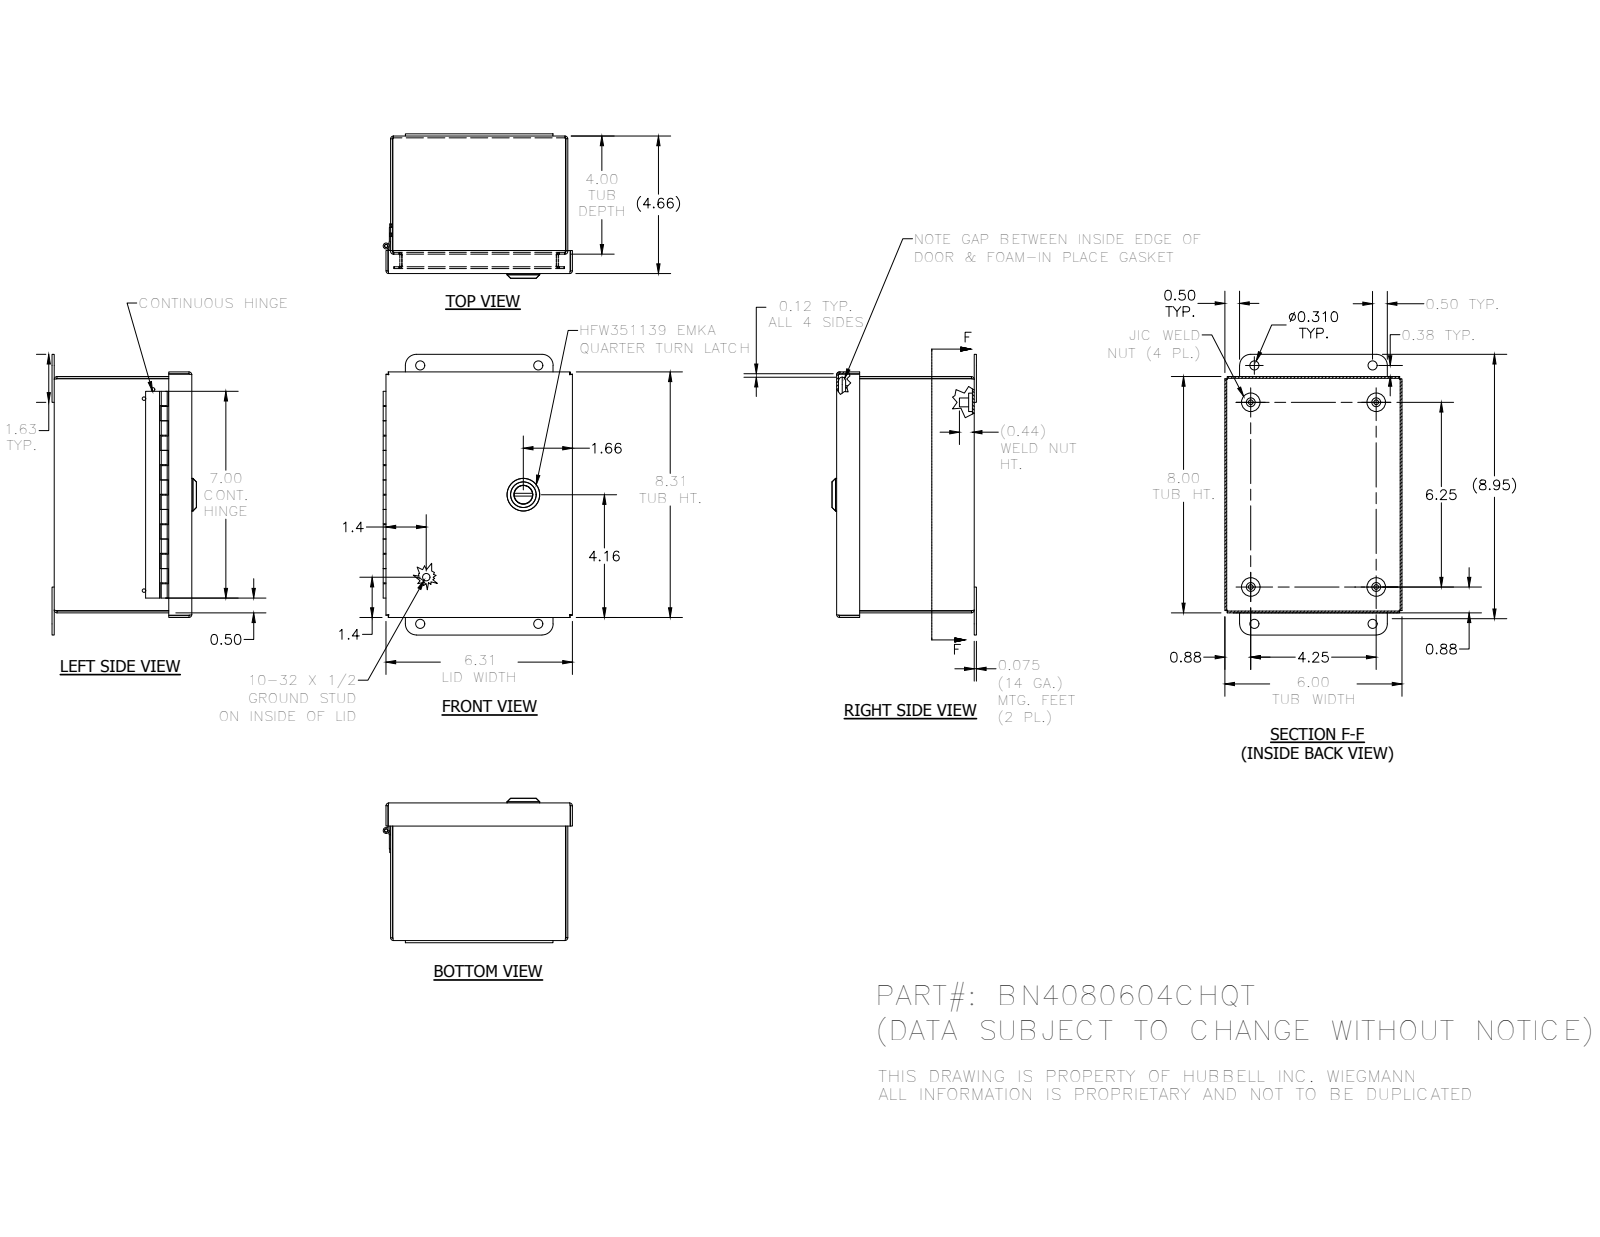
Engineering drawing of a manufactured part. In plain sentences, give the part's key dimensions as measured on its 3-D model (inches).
The part is named "BN4080604CHQT_a". Its 3-D file was written by "SolidWorks 2018 (AUTOMOTIVE_DESIGN)". It is 21 solids with 745 faces: 372 planar, 245 cylindrical and 128 other. Overall it measures 9.5 by 6.406 by 4.888 inches. Its volume is 20.9 cubic inches and its surface area 625 square inches. Round holes: 4 of diameter 0.156, 4 of diameter 0.31, 3 of diameter 0.12, 1 of diameter 0.116, 1 of diameter 0.197, 1 of diameter 0.315, 1 of diameter 0.394, 1 of diameter 0.402, 1 of diameter 0.634, 1 of diameter 0.802. Round bosses or shafts: 4 of diameter 0.3, 3 of diameter 0.625, 1 of diameter 1.102, 1 of diameter 0.866, 1 of diameter 0.78, 1 of diameter 0.625, 1 of diameter 0.622, 1 of diameter 0.598. Partial cylindrical surfaces (rounded edges, fillets, slot ends): 30 of radius 0.012, 20 of radius 0.031, 20 of radius 0.093, 16 of radius 0.125, 12 of radius 0.02, 4 of radius 0.157, 4 of radius 0.375, 2 of radius 0.016. The main face-to-face distances are 0.062, 0.062, 4.594, 4.656, 4.532, 4.594, 7.938, 5.938, 6, 5.876. The hole center spacings are 1.256, 4.31, 7.501, 8.559, 4, 4.25, 4.782, 6.25.
